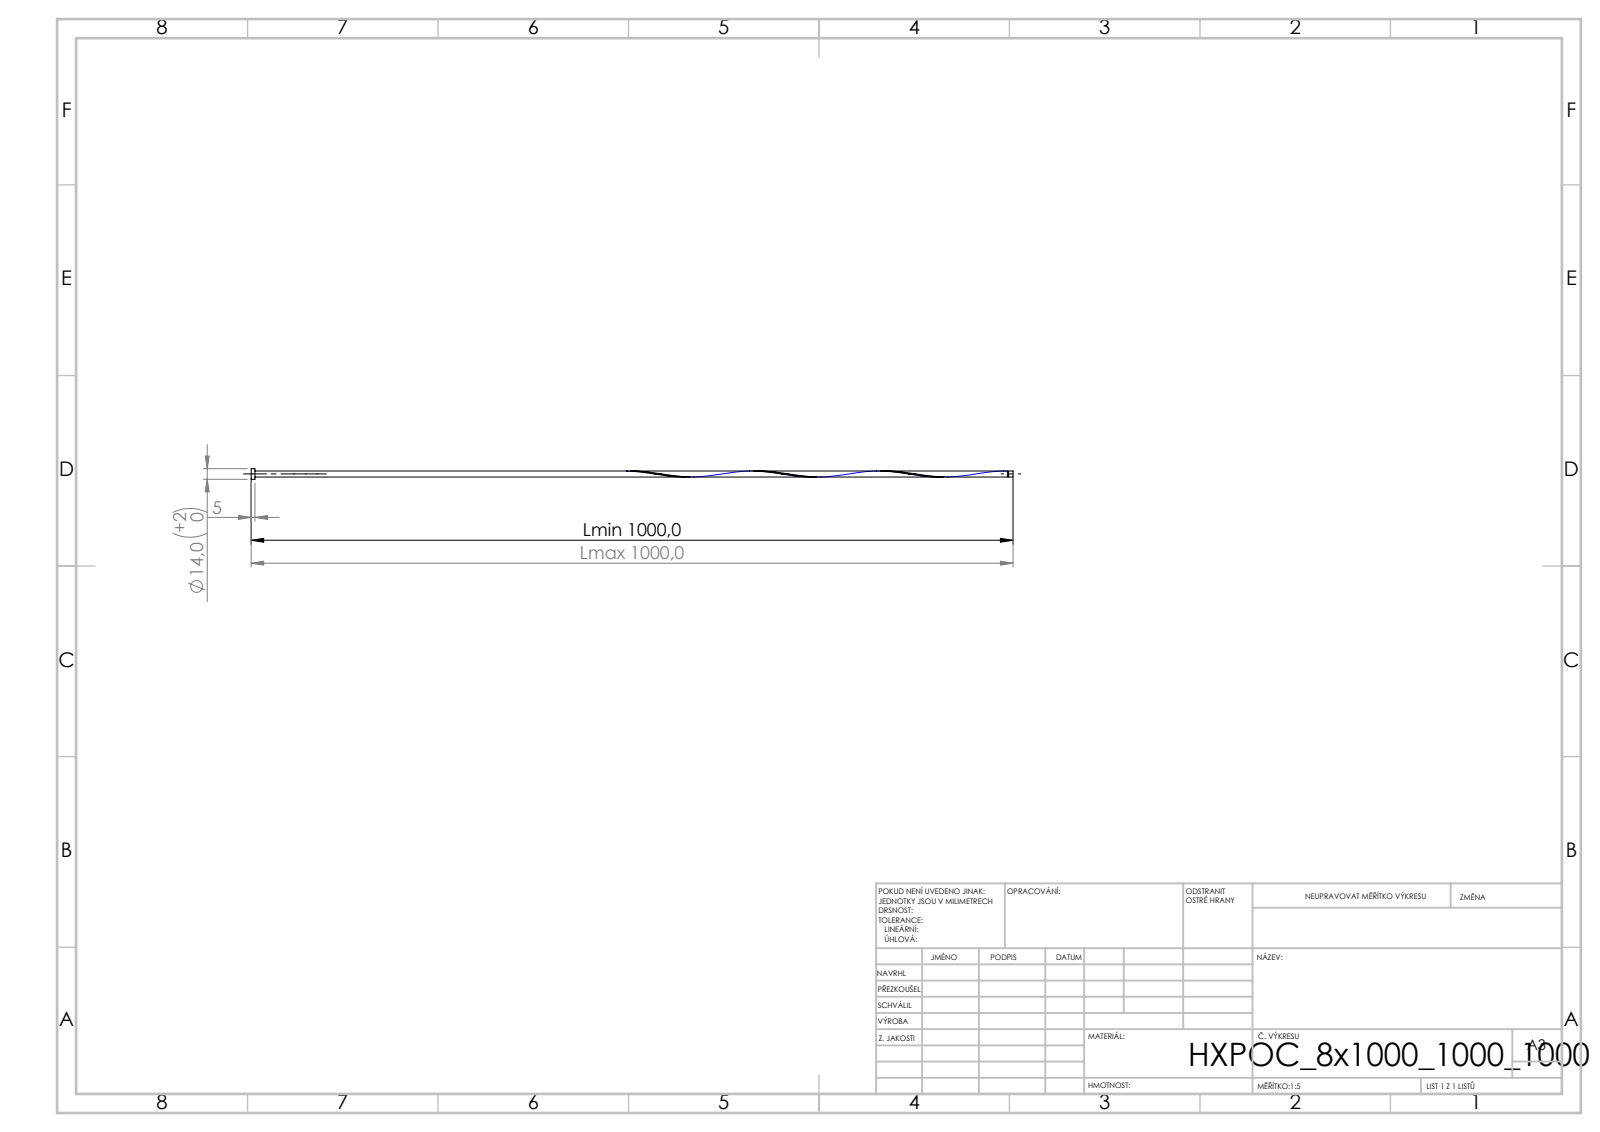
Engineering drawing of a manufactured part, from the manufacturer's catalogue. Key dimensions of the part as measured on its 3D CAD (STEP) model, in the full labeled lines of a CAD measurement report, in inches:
STEP written by: SolidWorks 2019 (CONFIG_CONTROL_DESIGN)
Units: inches
Bodies: 1 solid, 16 faces (6 planar, 9 cylindrical, 1 other)
Overall size (bounding box): 39.37 × 0.551 × 0.551
Volume: 3.75 in³ · Surface area: 53.2 in²
Round bosses / shafts (diameter × count): ⌀0.551 ×1, ⌀0.315 ×1, ⌀0.252 ×1
Main face-to-face distances: 0.197, 39.37, 39.173, 39.144, 38.948, 0.226, 39.081, 38.885, 0.063, 0.289
